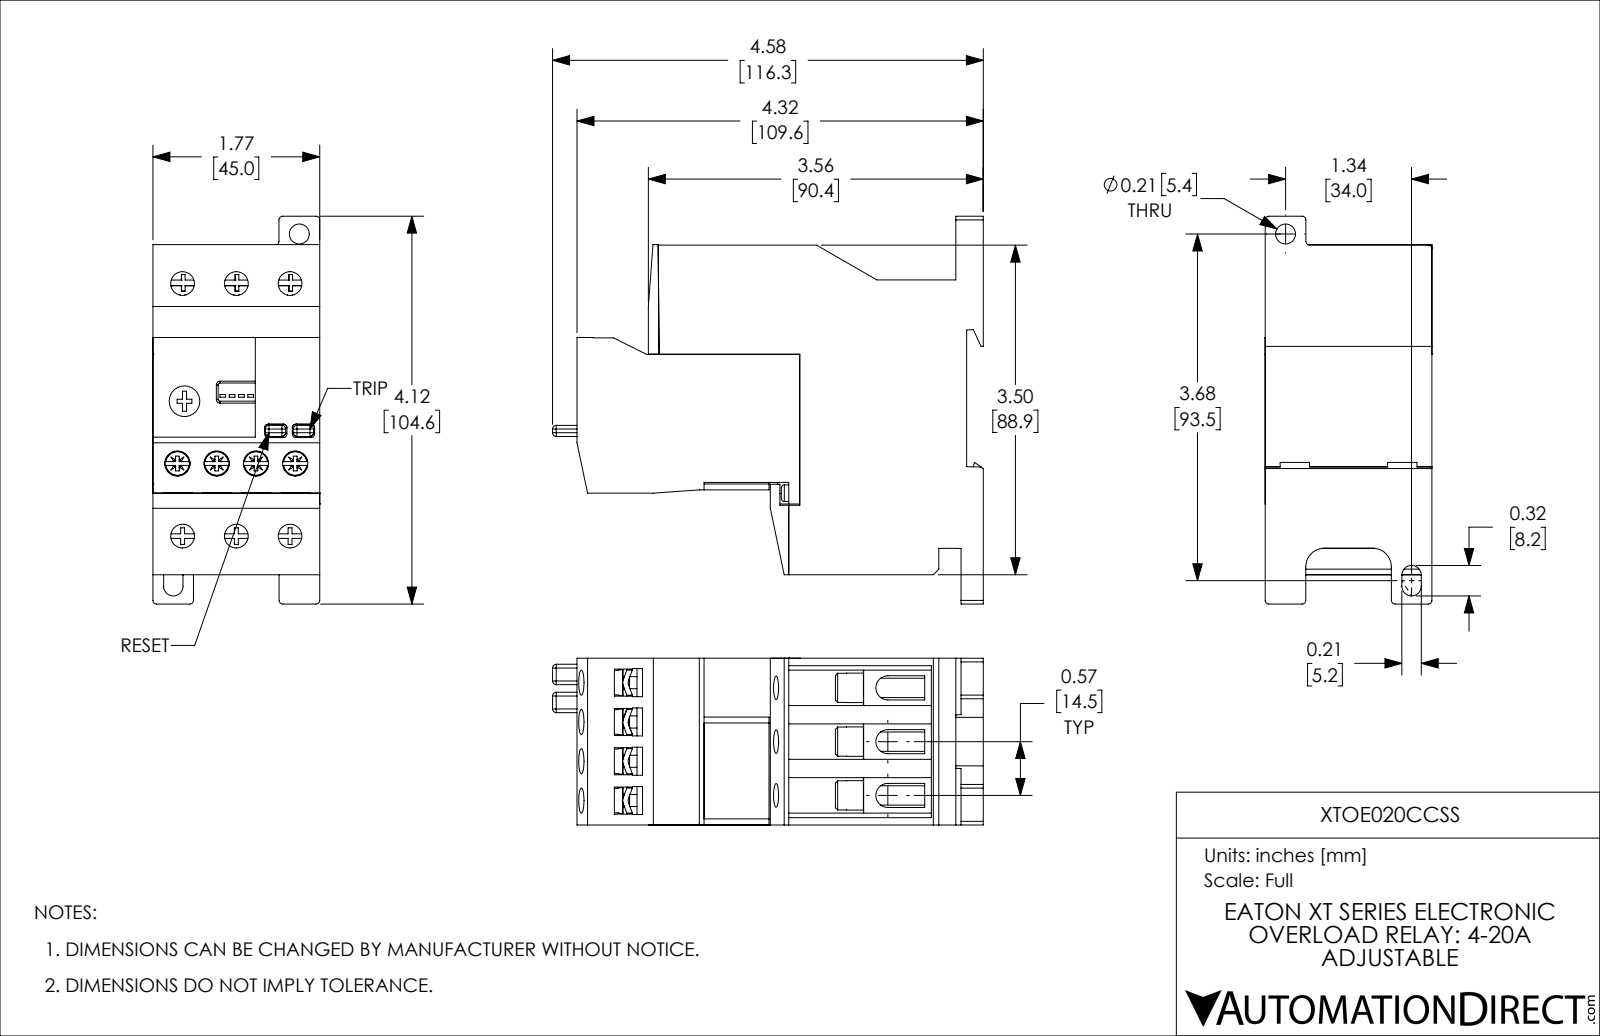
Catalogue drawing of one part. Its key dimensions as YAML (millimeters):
part_name: "XTOE020CCSS"
step_written_by: "SolidWorks 2018 (AUTOMOTIVE_DESIGN)"
units: millimeters
bodies: {solids: 42, faces: 1296, planar: 854, cylindrical: 281, other: 161}
overall_size: [116.25, 104.6, 45.01]
volume: 292500
surface_area: 75869
round_holes:
  - {diameter: 6.4, count: 6}
  - {diameter: 3.55, count: 5}
  - {diameter: 6.8, count: 4}
  - {diameter: 7.94, count: 3}
  - {diameter: 2.18, count: 2}
  - {diameter: 3.2, count: 2}
  - {diameter: 5.38, count: 1}
round_bosses_or_shafts:
  - {diameter: 3.4, count: 4}
  - {diameter: 3.25, count: 4}
  - {diameter: 2.8, count: 4}
  - {diameter: 2.5, count: 4}
  - {diameter: 8, count: 3}
  - {diameter: 4.5, count: 2}
  - {diameter: 8.27, count: 1}
partial_cylinders:
  - {radius: 0.5, count: 64}
  - {radius: 0.3, count: 24}
  - {radius: 1, count: 22}
  - {radius: 2, count: 10}
  - {radius: 3.25, count: 6}
  - {radius: 0.8, count: 4}
  - {radius: 0.4, count: 3}
  - {radius: 1.57, count: 2}
face_to_face_distances: [45, 14.5, 1.87, 10.89, 4.5, 45.01, 44.99, 29, 49.5, 16.37]
hole_center_spacings: [10.6, 21.2, 10.59, 10.61, 19.63, 48.55, 48.82, 51.07]
